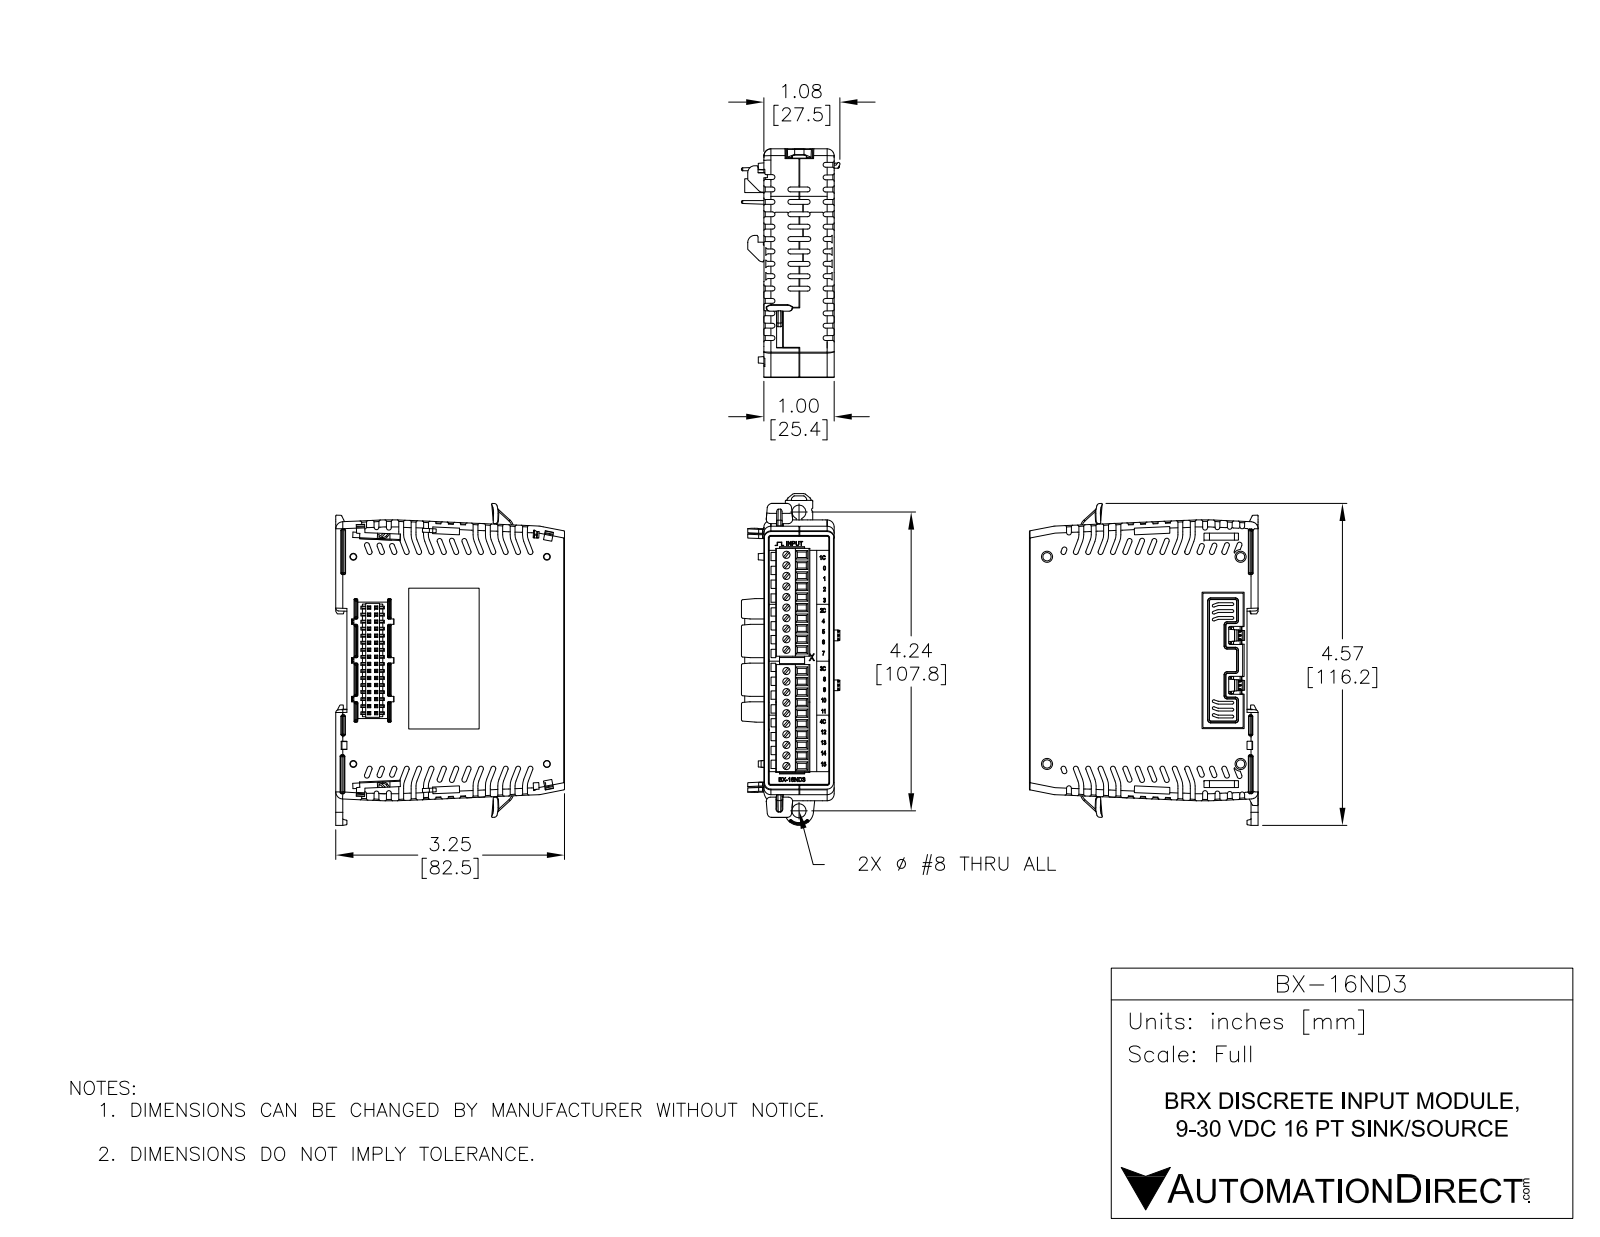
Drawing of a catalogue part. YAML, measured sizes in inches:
part_name: "BX-16ND3"
step_written_by: "SolidWorks 2017 (AUTOMOTIVE_DESIGN)"
units: inches
bodies: {solids: 12, faces: 4168, planar: 2931, cylindrical: 663, other: 574}
overall_size: [4.586, 3.25, 1.402]
volume: 11.58
surface_area: 72.51
round_holes:
  - {diameter: 0.047, count: 2}
  - {diameter: 0.065, count: 2}
  - {diameter: 0.118, count: 2}
  - {diameter: 0.118, count: 2}
  - {diameter: 0.199, count: 1}
round_bosses_or_shafts:
  - {diameter: 0.062, count: 2}
  - {diameter: 0.059, count: 2}
partial_cylinders:
  - {radius: 0.005, count: 102}
  - {radius: 0.008, count: 101}
  - {radius: 0.01, count: 47}
  - {radius: 0.02, count: 34}
  - {radius: 0.005, count: 24}
  - {radius: 0.062, count: 20}
  - {radius: 0.117, count: 14}
  - {radius: 0.039, count: 13}
face_to_face_distances: [1, 3.211, 3.22, 0.475, 0.039, 0.157, 3.053, 3.063, 0.1, 0.787]
hole_center_spacings: [0.1, 0.824, 0.919, 1.3, 2.093, 2.193, 2.585, 2.617]
